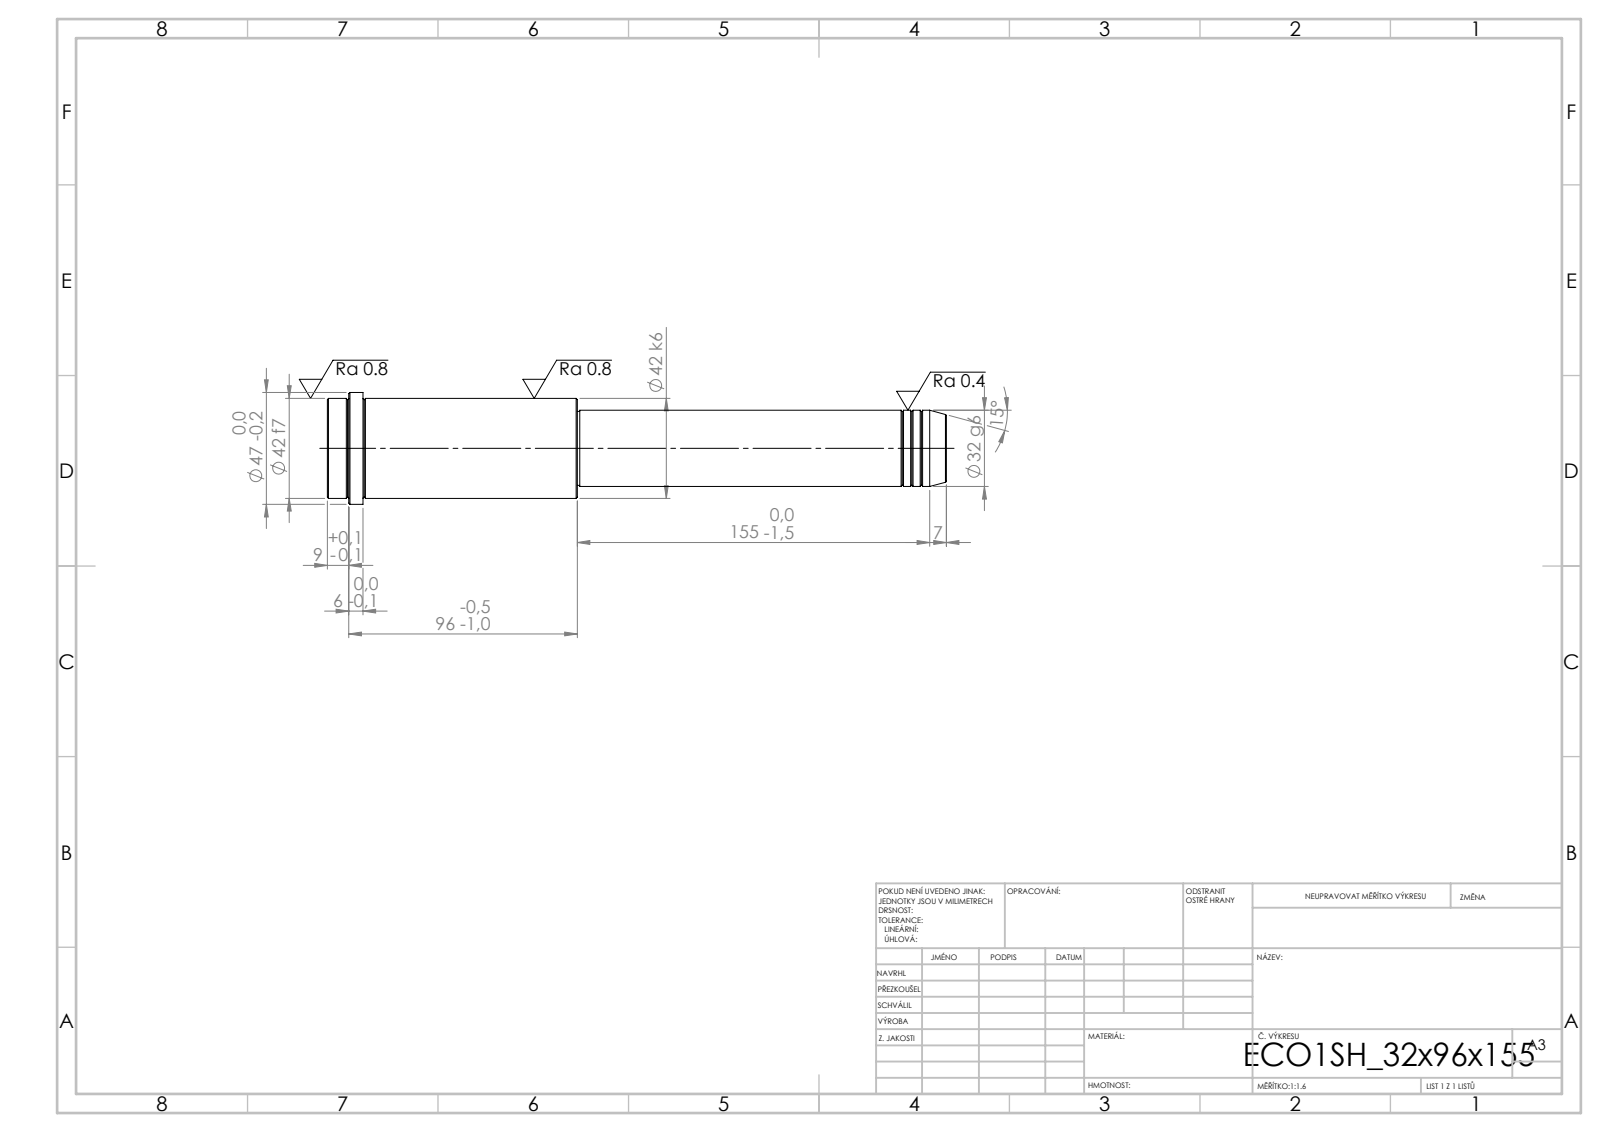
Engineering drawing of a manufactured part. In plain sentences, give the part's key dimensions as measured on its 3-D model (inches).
Its 3-D file was written by "SolidWorks 2019 (CONFIG_CONTROL_DESIGN)". It is 1 solid with 52 faces: 6 planar, 16 cylindrical and 30 other. Overall it measures 10.236 by 1.85 by 1.85 inches. Its volume is 16.55 cubic inches and its surface area 51.27 square inches. Round bosses or shafts: 1 of diameter 1.85, 1 of diameter 1.654, 1 of diameter 1.26, 1 of diameter 1.22. The main face-to-face distances are 10.236, 6.102, 4.134, 9.646, 3.543, 0.591, 9.882, 3.78, 0.236, 0.354.
